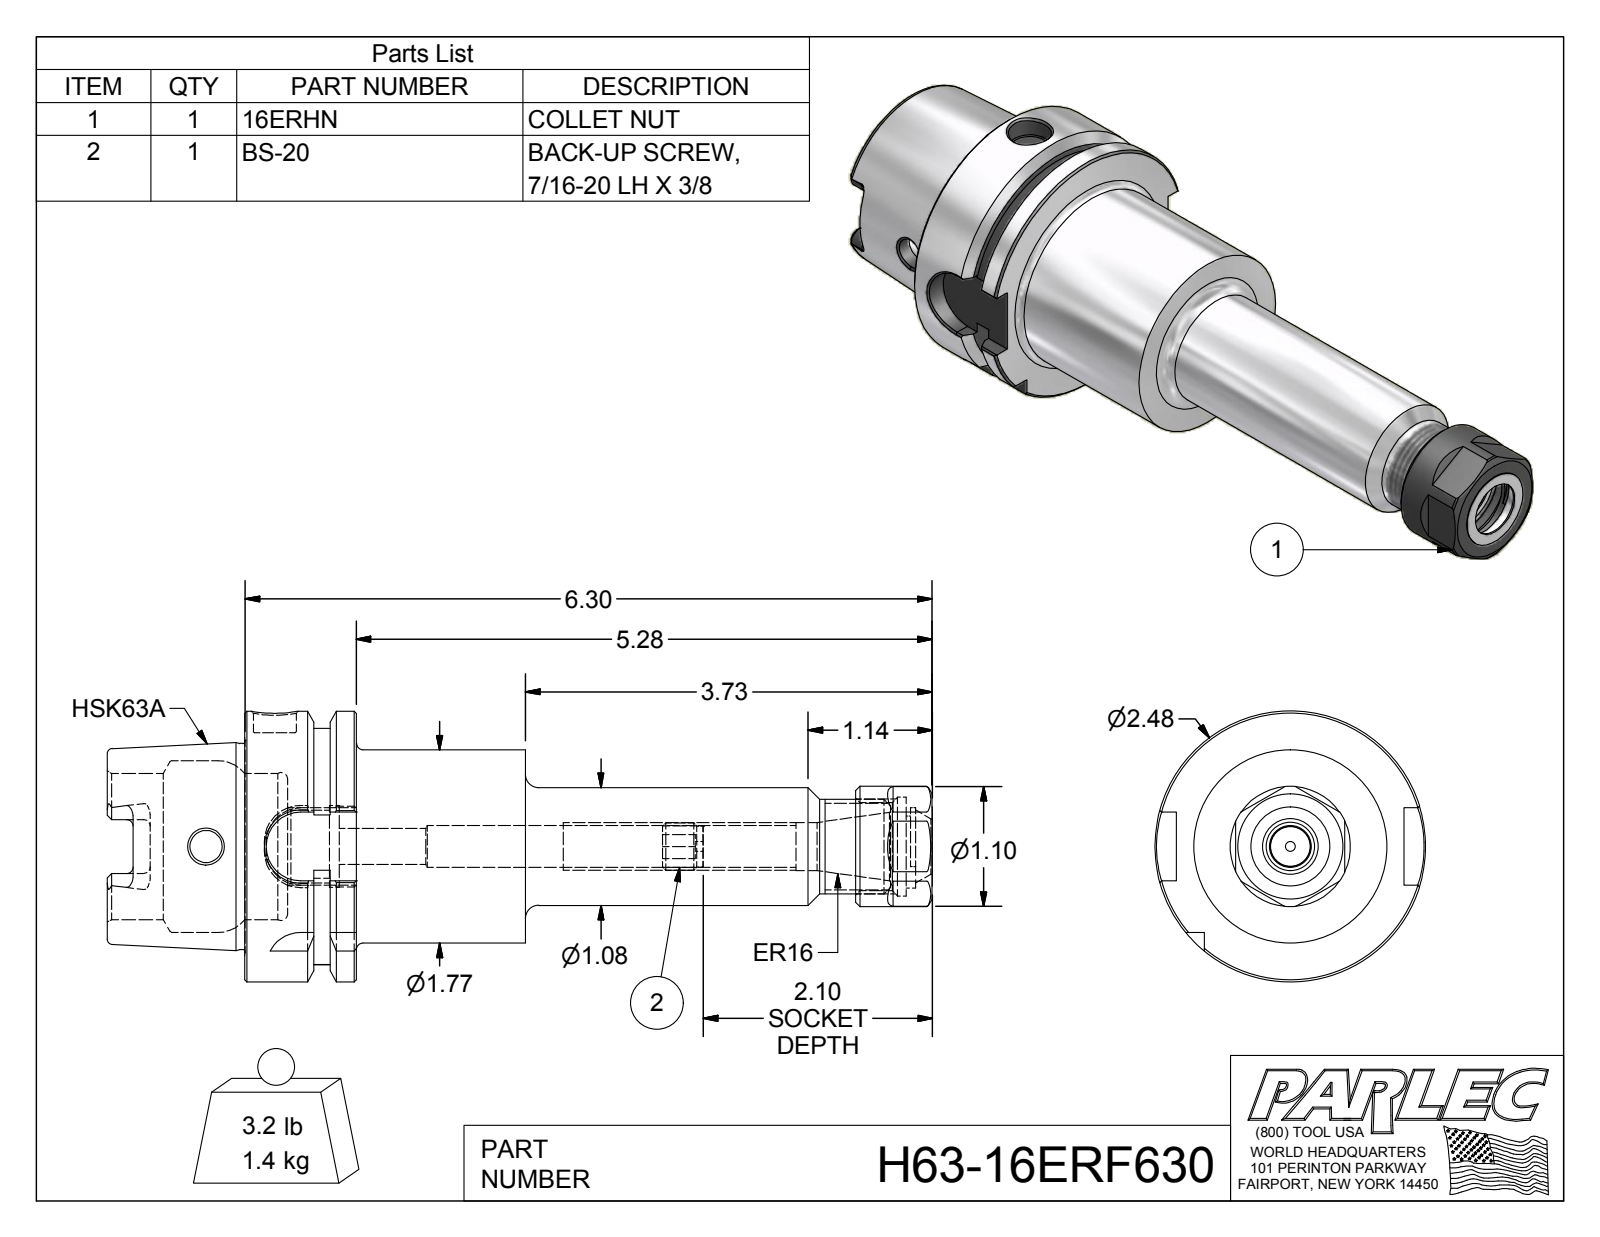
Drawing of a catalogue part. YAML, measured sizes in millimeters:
part_name: "H63-16ER6-1; 16ERHN; BS-20; H63-16ERF630"
step_written_by: "Autodesk Inventor 2016 (AUTOMOTIVE_DESIGN)"
units: millimeters
bodies: {solids: 3, faces: 189, planar: 78, cylindrical: 47, other: 64}
overall_size: [192.02, 63, 63]
volume: 146714
surface_area: 40521
round_holes:
  - {diameter: 2.29, count: 1}
  - {diameter: 7.5, count: 1}
  - {diameter: 8.4, count: 1}
  - {diameter: 9.73, count: 1}
  - {diameter: 10, count: 1}
  - {diameter: 11.18, count: 1}
  - {diameter: 12.4, count: 1}
  - {diameter: 16.92, count: 1}
  - {diameter: 17.02, count: 1}
  - {diameter: 19.02, count: 1}
  - {diameter: 20.5, count: 1}
  - {diameter: 23, count: 1}
round_bosses_or_shafts:
  - {diameter: 63, count: 1}
  - {diameter: 48.04, count: 1}
  - {diameter: 28, count: 1}
  - {diameter: 27.43, count: 1}
  - {diameter: 22, count: 1}
  - {diameter: 10.97, count: 1}
  - {diameter: 9.46, count: 1}
partial_cylinders:
  - {radius: 1.5, count: 6}
  - {radius: 2.88, count: 4}
  - {radius: 8, count: 4}
  - {radius: 7.24, count: 1}
  - {radius: 9, count: 1}
  - {radius: 27.5, count: 1}
face_to_face_distances: [26, 10, 16, 32, 42, 58, 192.02, 160.02, 150.02, 134.02]
hole_center_spacings: [1.52]
